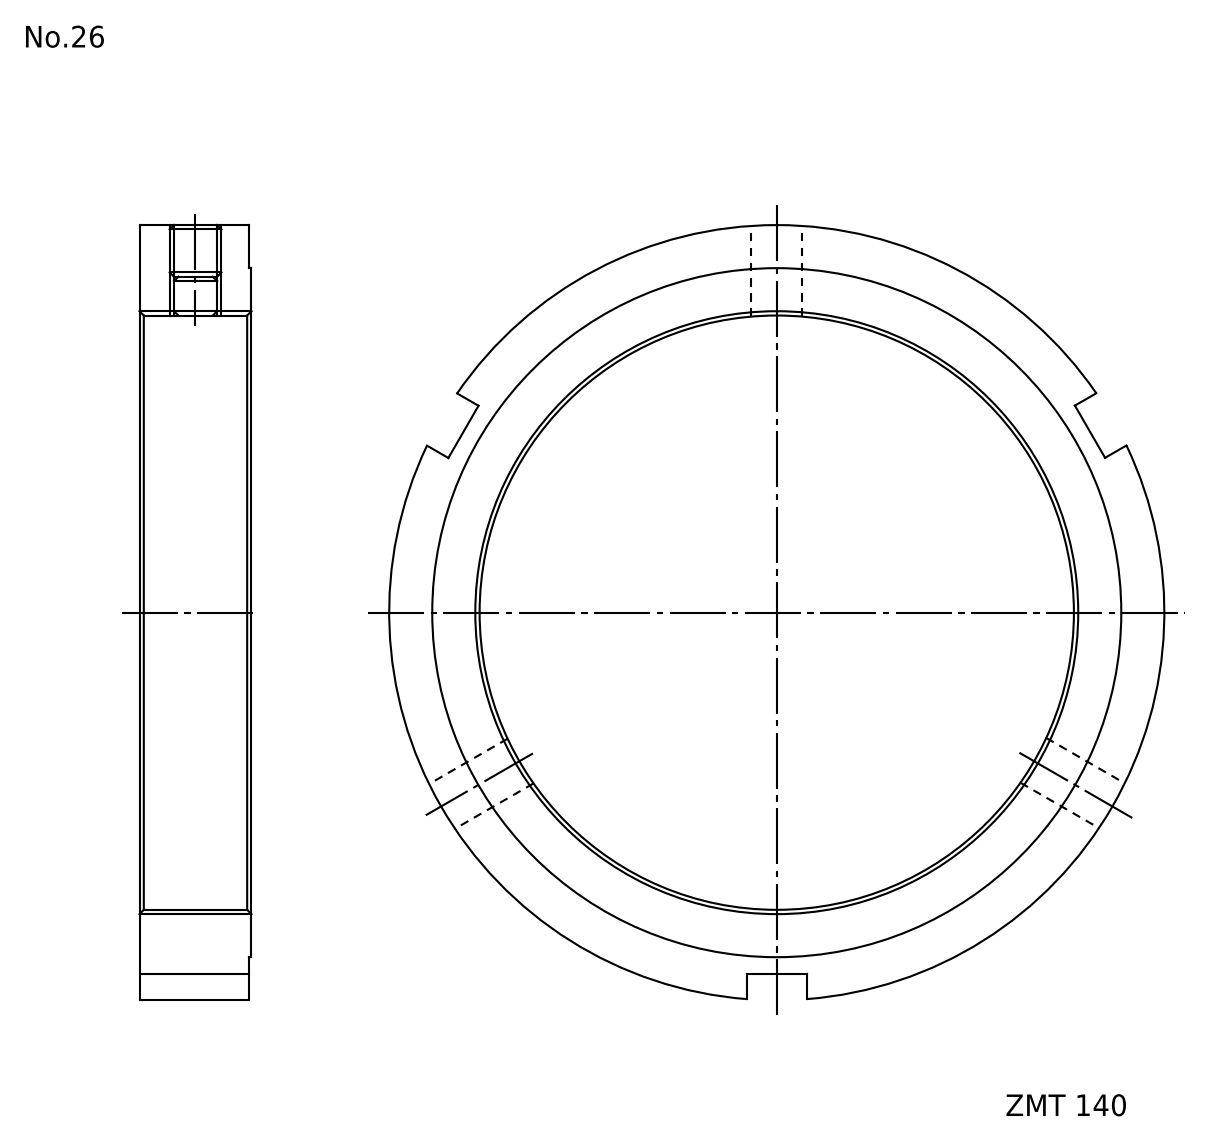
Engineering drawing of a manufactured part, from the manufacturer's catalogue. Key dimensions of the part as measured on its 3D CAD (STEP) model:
Part name (STEP PRODUCT): FKD ZMT140
STEP written by: Autodesk Inventor 2011 (AUTOMOTIVE_DESIGN)
Units: millimetres
Bodies: 1 solid, 20 faces (12 planar, 8 cylindrical, 0 other)
Overall size (bounding box): 180 × 179.73 × 26
Volume: 247 568 mm³ · Surface area: 48 017 mm²
Round holes (diameter × count): ⌀10.11 ×3, ⌀140 ×1
Round bosses / shafts (diameter × count): ⌀180 ×1, ⌀160 ×1
Main face-to-face distances: 25.5, 0.5, 26, 14
